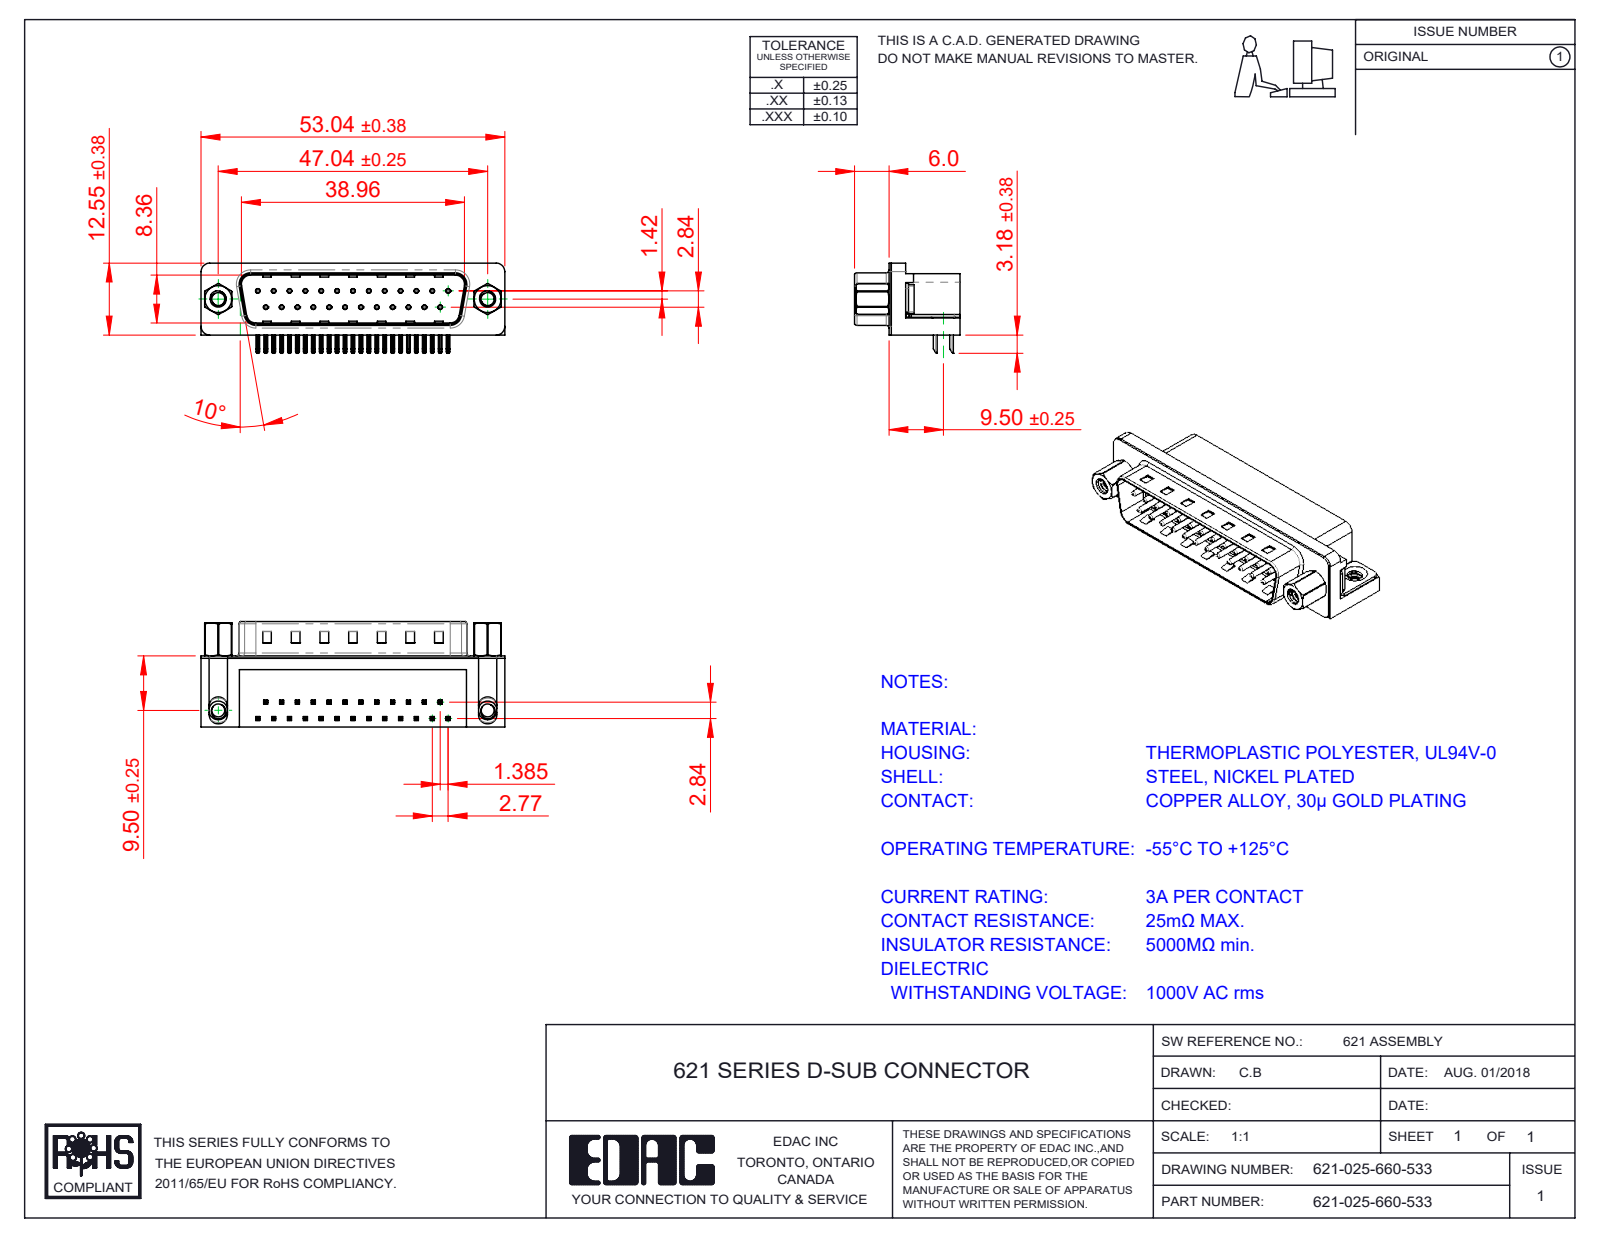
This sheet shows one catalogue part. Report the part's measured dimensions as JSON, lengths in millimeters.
{"part_name": "621 4-40 Hex Standoff 5; 621 4-40 Threaded Rivet; 621 Housing_25 Socket; 621 2 Prong Board Lock (+4 more)", "step_written_by": "SolidWorks 2016 (CONFIG_CONTROL_DESIGN)", "units": "millimeters", "bodies": {"solids": 33, "faces": 2429, "planar": 1459, "cylindrical": 739, "other": 231}, "overall_size": [53.04, 18.4, 16.25], "volume_mm3": 6560, "surface_area_mm2": 8171, "round_holes": [[0.35, 25], [0.8, 25], [2.26, 2], [2.29, 2], [4, 2], [4.8, 2], [5, 2]], "round_bosses_or_shafts": [[0.75, 25], [4.9, 2], [4.75, 2], [3.9, 2], [2.79, 2]], "partial_cylinders_radius": [[0.25, 108], [0.12, 50], [1, 16], [0.5, 14], [1.6, 8], [1.5, 7], [0.32, 4], [0.9, 4]], "face_to_face_distances": [0.4, 12, 10.35, 2.1, 8.76, 10.46, 10.86, 1.7, 12.4, 9], "hole_center_spacings": [3.16, 2.77, 5.54, 8.31, 11.08, 13.85, 16.62, 5.03]}
